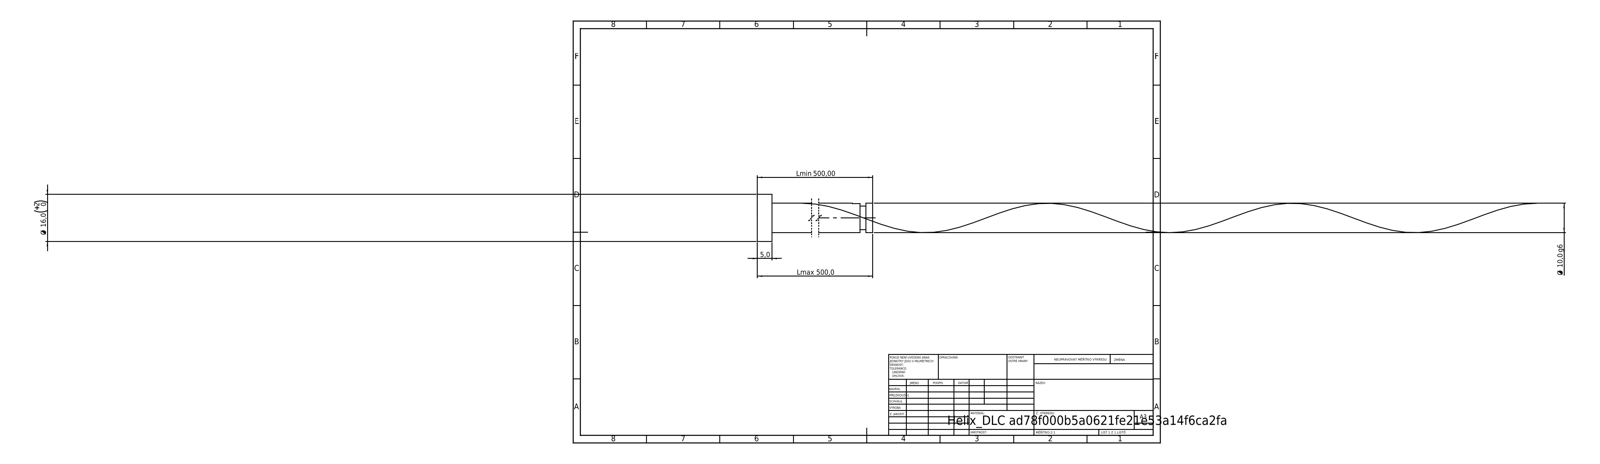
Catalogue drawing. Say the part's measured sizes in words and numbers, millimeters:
Its 3-D file was written by "SolidWorks 2019 (CONFIG_CONTROL_DESIGN)". It is 1 solid with 21 faces: 6 planar, 14 cylindrical and 1 other. Overall it measures 500 by 16 by 16 millimeters. Its volume is 39 450 cubic millimeters and its surface area 16 507 square millimeters. Round bosses or shafts: 1 of diameter 16, 1 of diameter 10, 1 of diameter 8. The main face-to-face distances are 5, 500, 495, 497.73, 492.73, 2.27, 495.73, 490.73, 2, 4.27.
